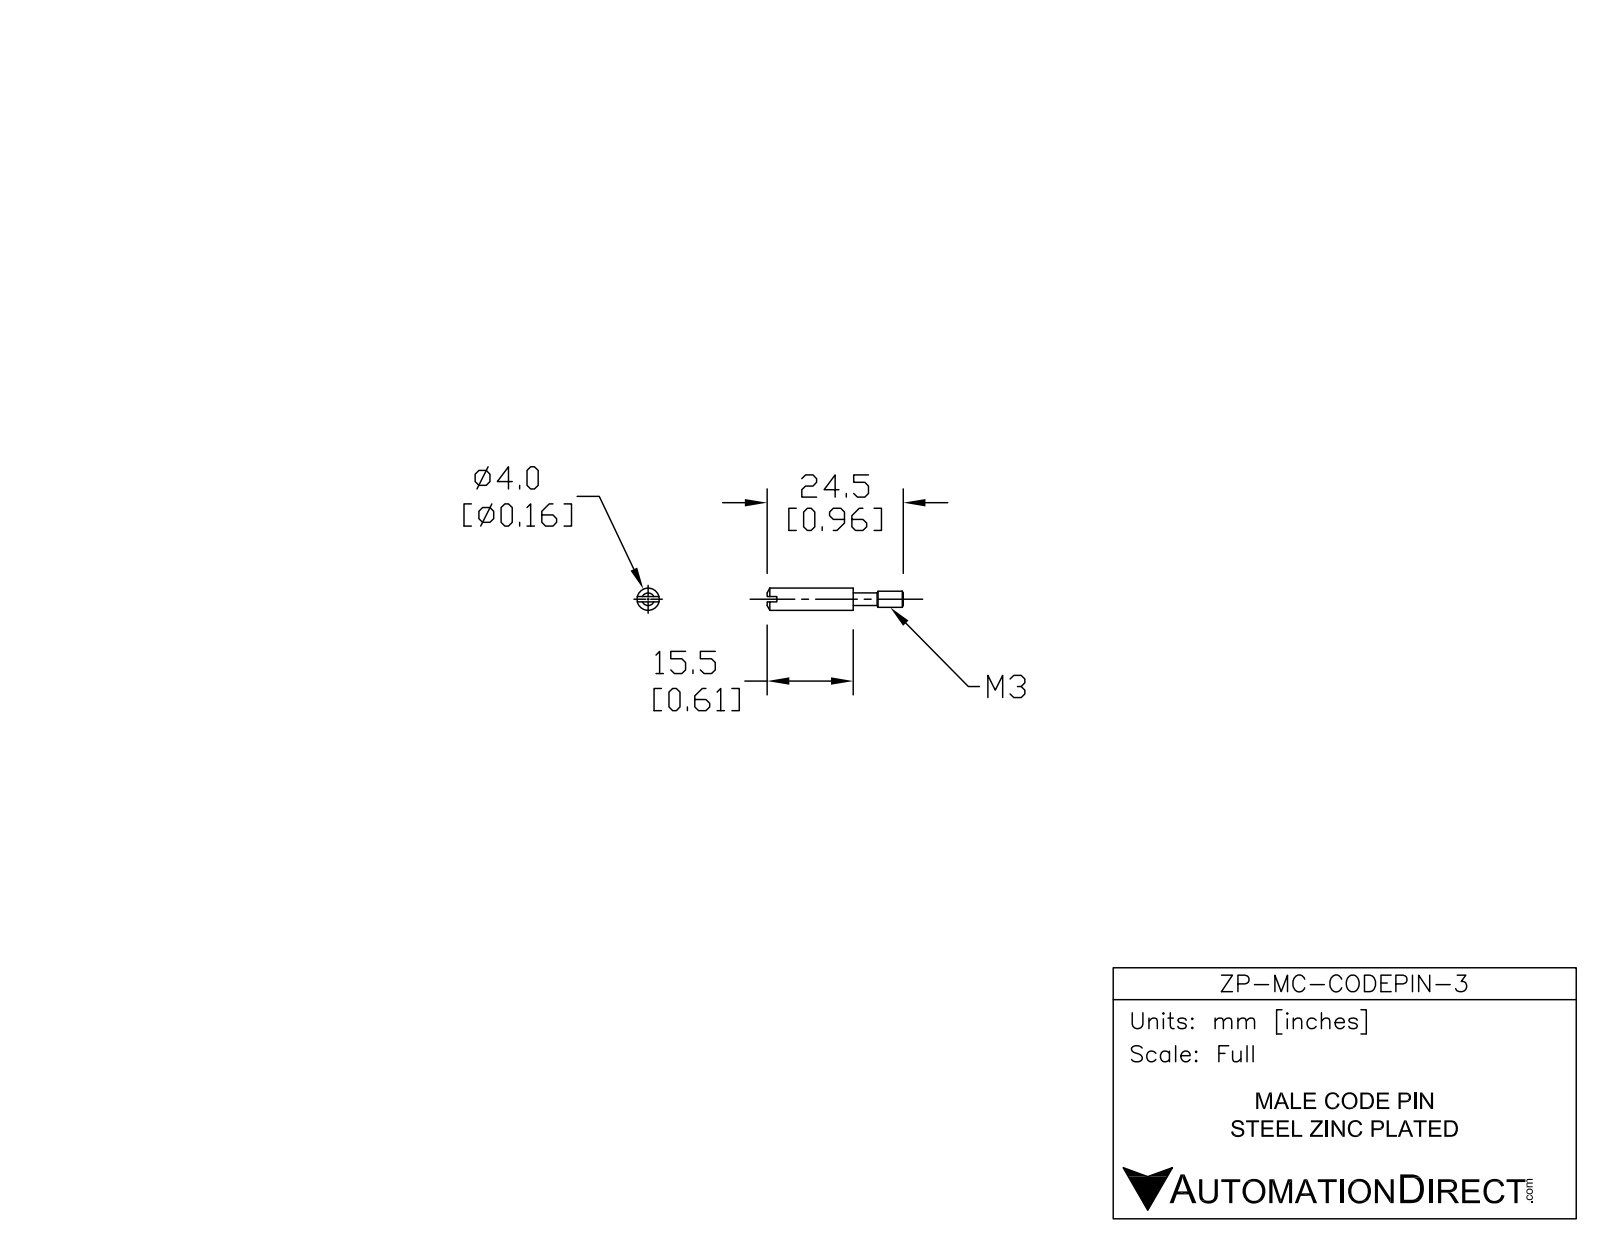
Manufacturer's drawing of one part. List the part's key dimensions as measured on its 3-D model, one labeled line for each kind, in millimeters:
Part name (STEP PRODUCT): ZP-MC-CODEPIN-3
STEP written by: SolidWorks 2014 (AUTOMOTIVE_DESIGN)
Units: millimetres
Bodies: 1 solid, 19 faces (7 planar, 6 cylindrical, 6 other)
Overall size (bounding box): 24.5 × 4 × 4
Volume: 234 mm³ · Surface area: 301 mm²
Round bosses / shafts (diameter × count): ⌀4 ×1, ⌀2.9 ×1, ⌀2.28 ×1
Main face-to-face distances: 0.96, 9, 22.75, 13.75, 24.5, 15.5, 1.75
